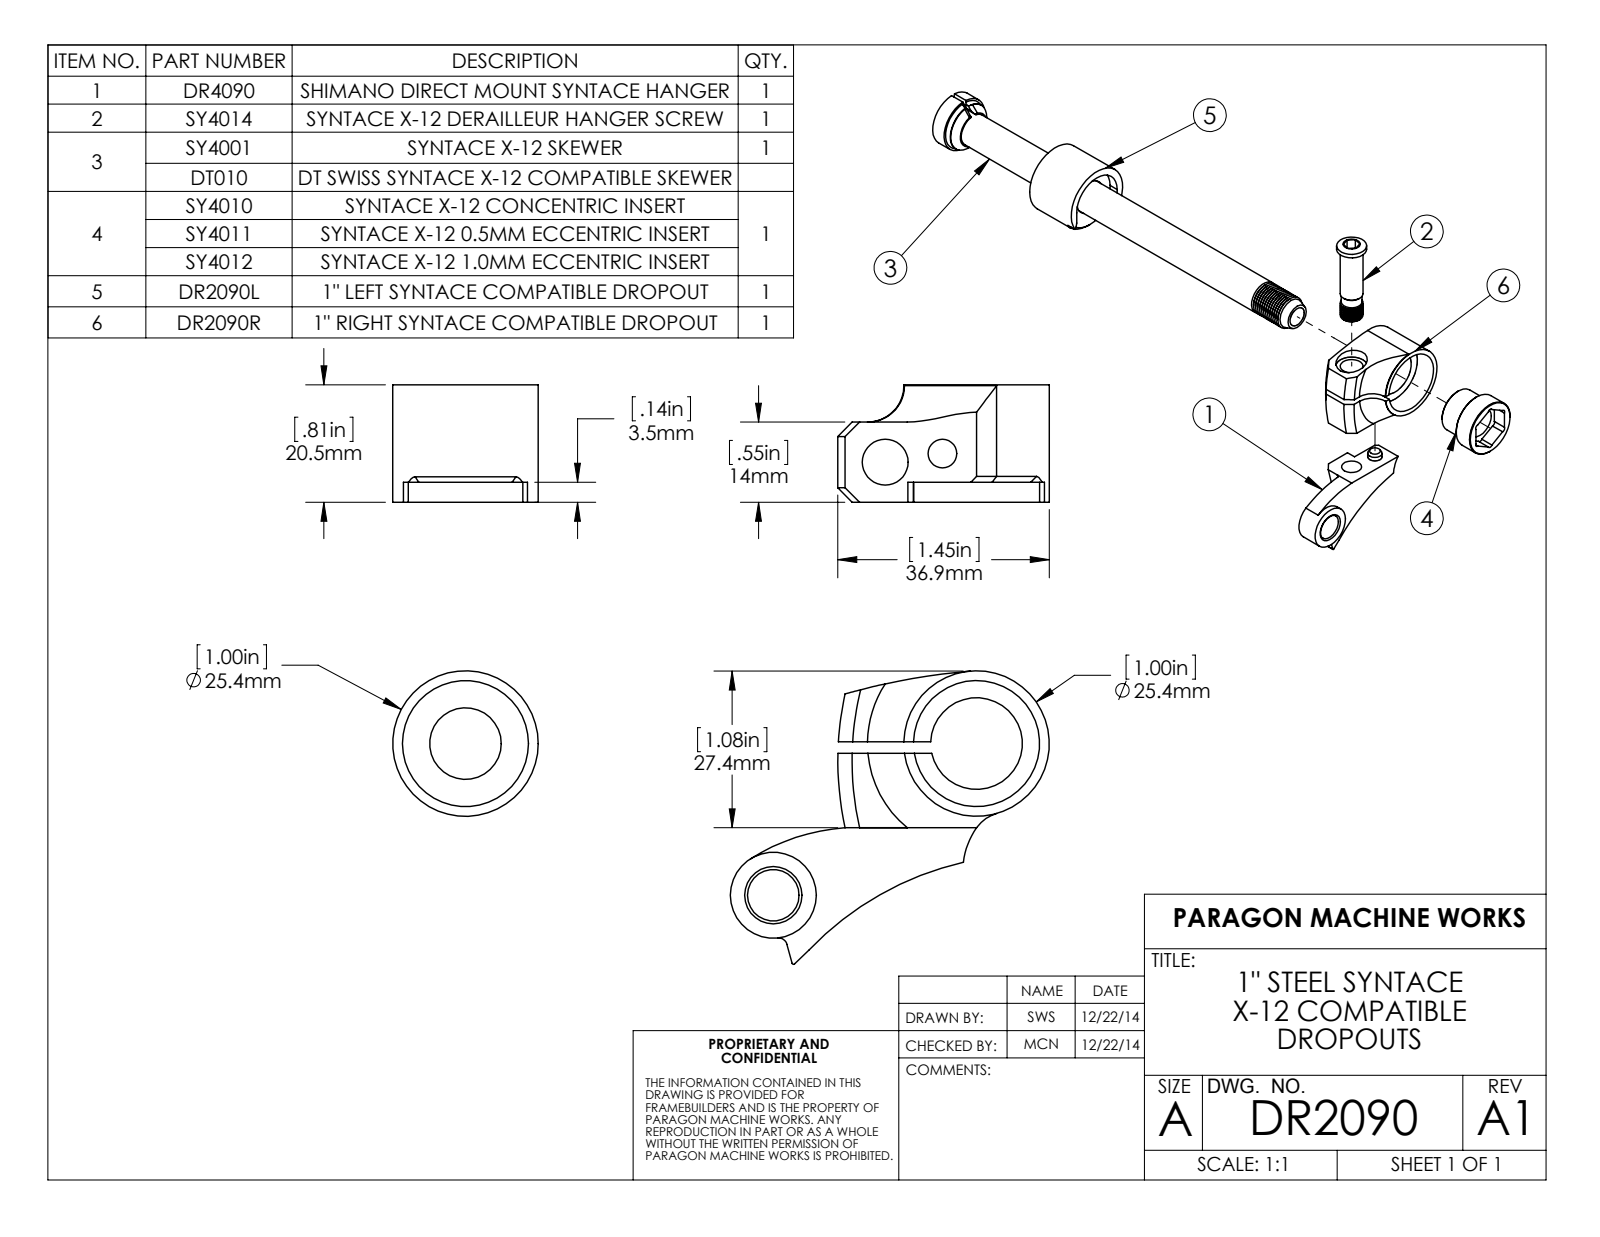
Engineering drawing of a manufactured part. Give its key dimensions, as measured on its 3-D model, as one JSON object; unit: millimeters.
{"part_name": "cone_for_12mm_axle_ver-02; stainless_steel_washer_12mm; DR4090; SY4014 (+5 more)", "step_written_by": "SolidWorks 2014 (AUTOMOTIVE_DESIGN)", "units": "millimeters", "bodies": {"solids": 8, "faces": 321, "planar": 69, "cylindrical": 97, "other": 155}, "overall_size": [177.67, 55.69, 51.24], "volume_mm3": 33600, "surface_area_mm2": 26369, "round_holes": [[7, 2], [11, 2], [4, 1], [5, 1], [8, 1], [9, 1], [12, 1], [12.5, 1], [16, 1], [22, 1]], "round_bosses_or_shafts": [[15, 2], [25.4, 1], [20, 1], [17.7, 1], [16.05, 1], [15.4, 1], [10.5, 1], [7.25, 1]], "partial_cylinders_radius": [[1, 9], [2.5, 3], [3.61, 2], [0.25, 1], [1.5, 1], [6.49, 1], [13, 1], [35.52, 1]], "face_to_face_distances": [4.5, 3.5, 8, 12.5, 14, 10.5, 1.5, 138.25, 2, 6], "hole_center_spacings": [10.11, 44.27]}
